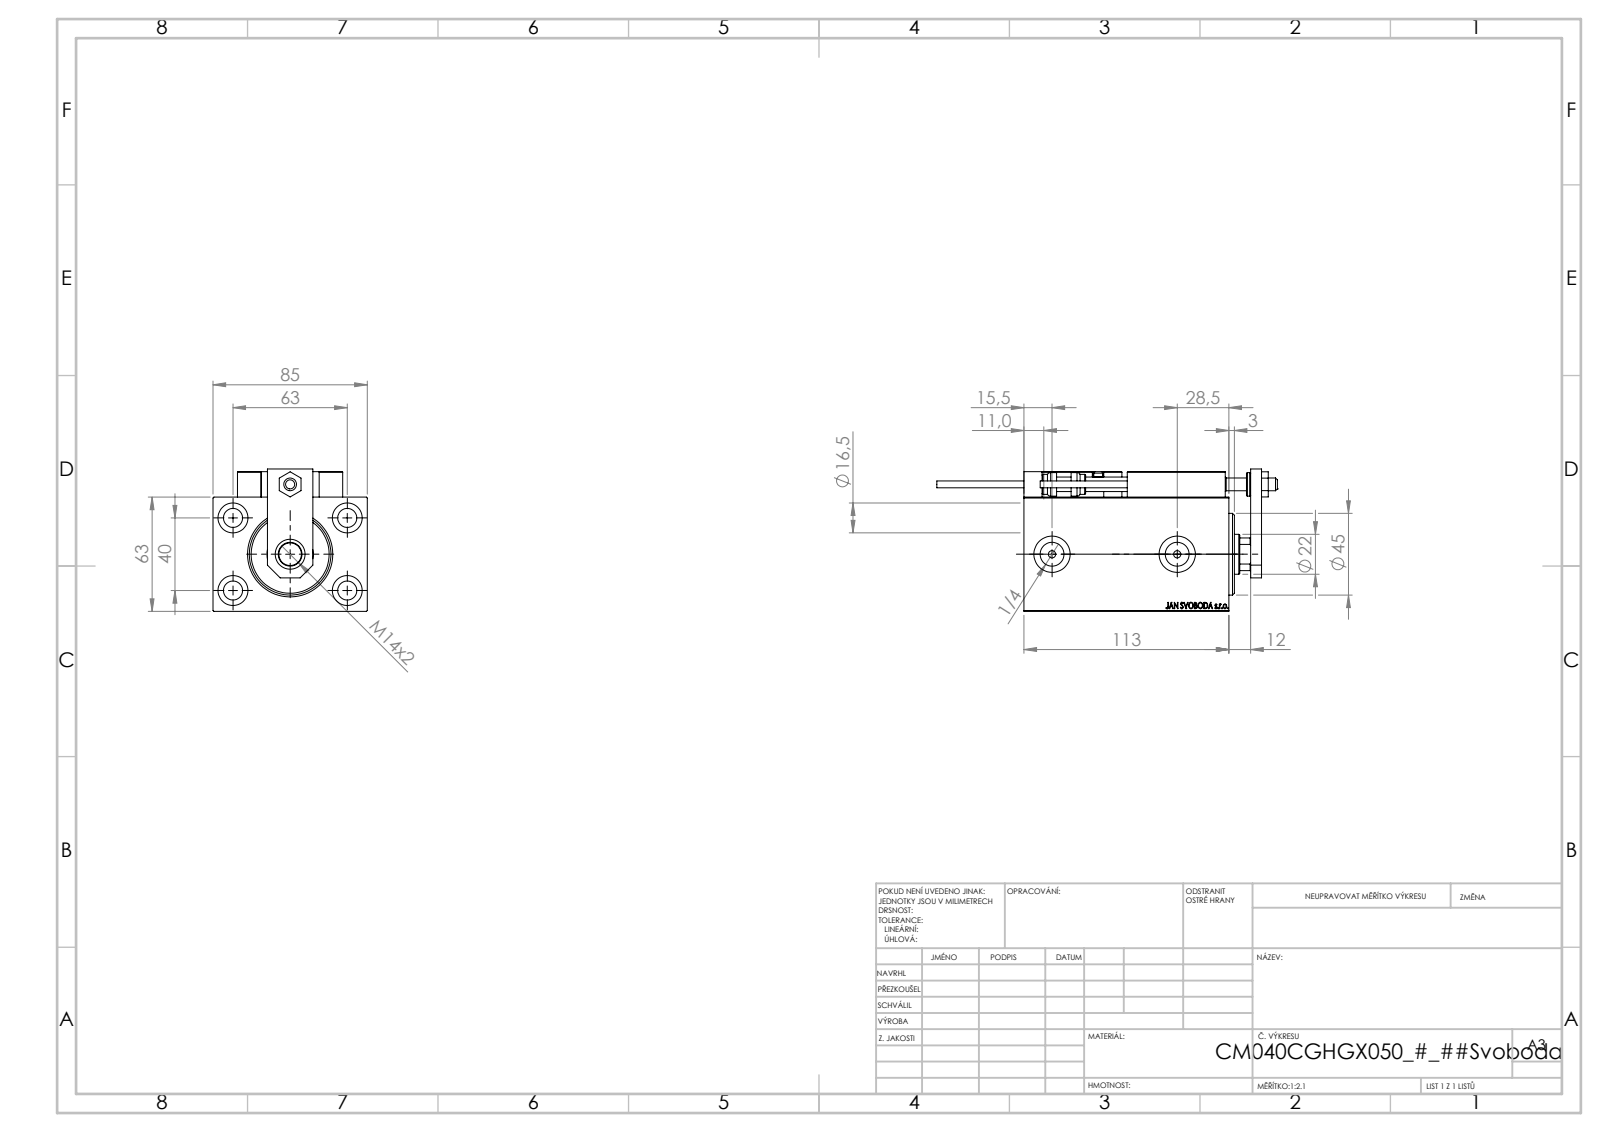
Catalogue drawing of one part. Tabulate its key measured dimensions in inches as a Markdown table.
| quantity | value |
| --- | --- |
| part name | ALLEN BOLT D5; MAGNET; KONCOVKA; ZARAZKA (+7 more) |
| STEP written by | SolidWorks 2019 (CONFIG_CONTROL_DESIGN) |
| units | inches |
| bodies | 23 solids, 1282 faces (560 planar, 188 cylindrical, 534 other) |
| overall size | 7.39 × 3.346 × 3.091 |
| volume | 34.29 in³ |
| surface area | 182.9 in² |
| round holes (diameter × count) | 0.157 × 6, 0.315 × 5, 0.65 × 5, 0.126 × 4, 0.413 × 4, 0.197 × 2, 0.518 × 2, 0.787 × 2, 0.276 × 1, 0.492 × 1, 0.866 × 1, 1.004 × 1 |
| round bosses / shafts (diameter × count) | 0.197 × 2, 0.15 × 2, 0.512 × 1, 0.433 × 1 |
| partial cylindrical surfaces (radius × count) | 0.012 × 30, 0.118 × 2, 0.413 × 1 |
| main face-to-face distances | 2.48, 3.346, 0.472, 3.976, 4.449, 0.551, 3.031, 0.591, 0.236, 0.709 |
| hole center spacings | 1.469, 0.448, 0.787, 1.165, 1.169, 1.42, 1.438, 1.575 |
